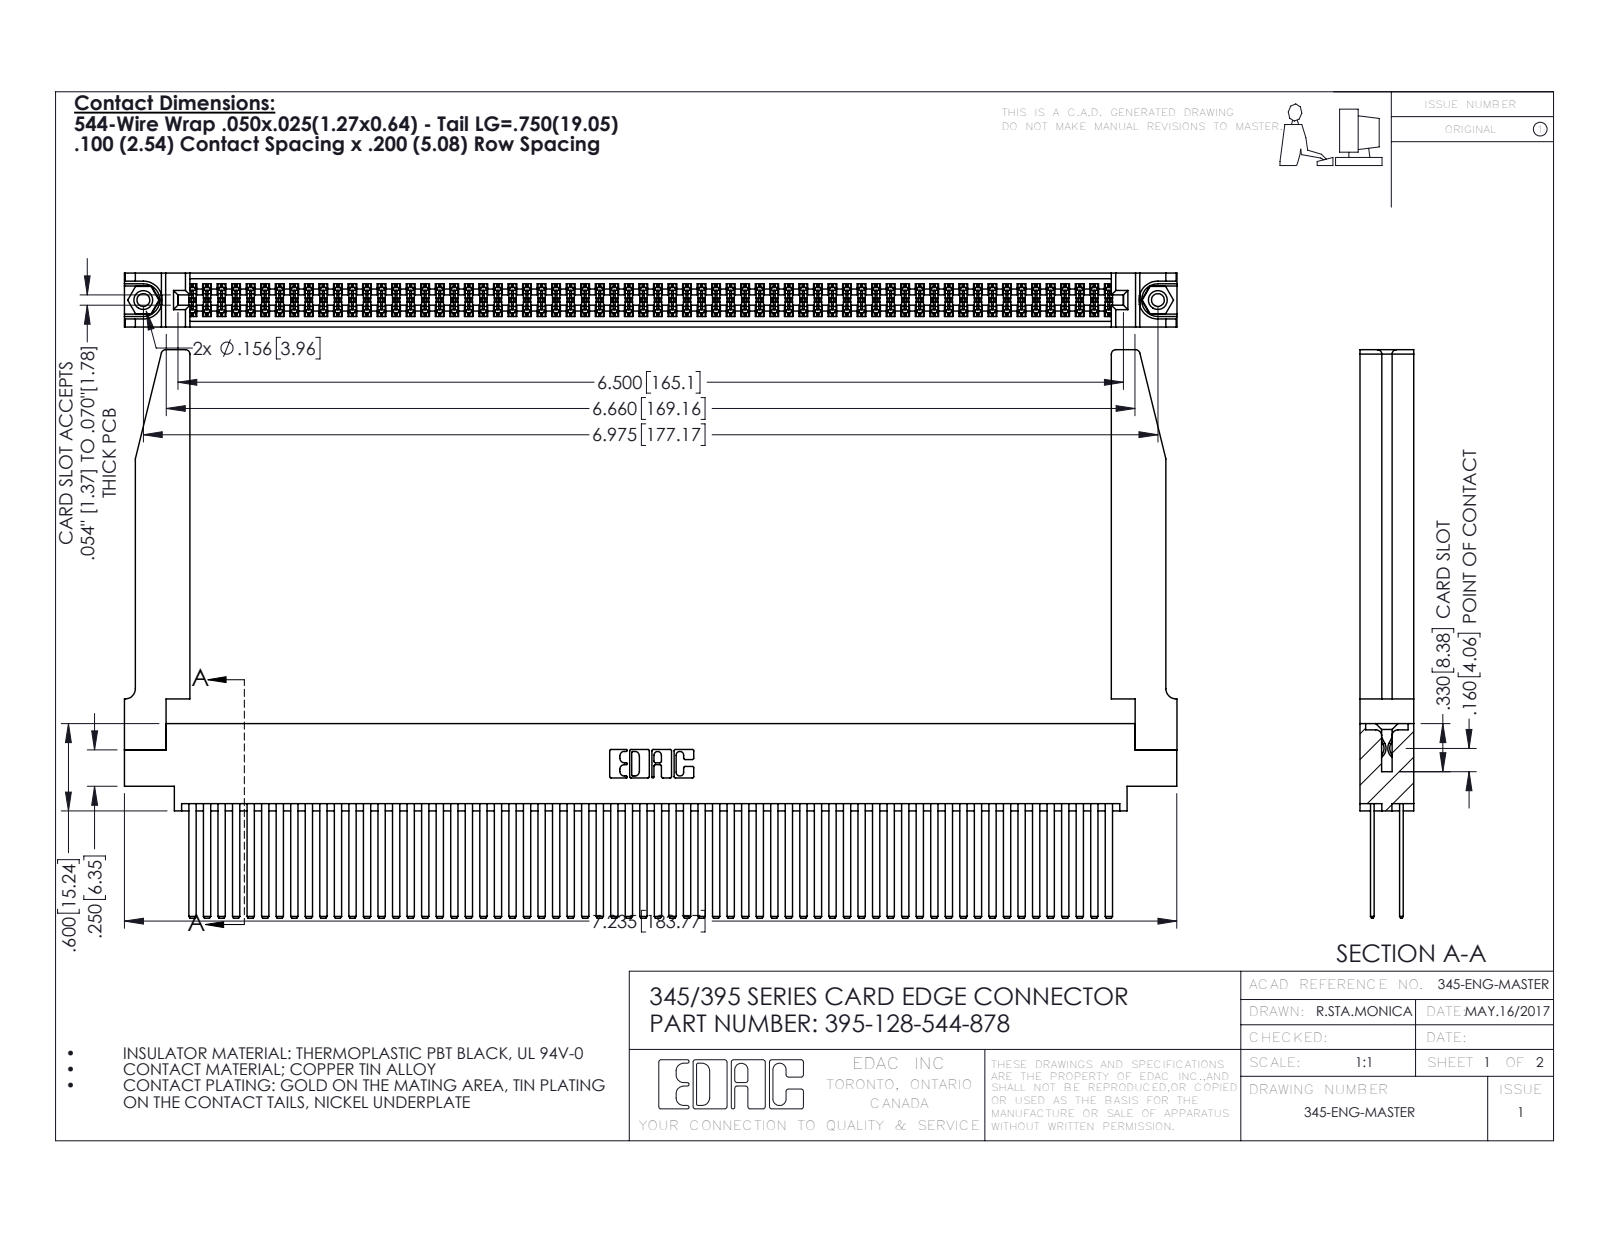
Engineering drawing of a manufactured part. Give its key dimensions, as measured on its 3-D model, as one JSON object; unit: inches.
{"part_name": "345-292-001_345-293-144; 345 Part_0.170 Offset - 0.156 Dia-TH; 345-220-078_345-220-078; 345-250-001_345-250-001-102 (+1 more)", "step_written_by": "SolidWorks 2016 (CONFIG_CONTROL_DESIGN)", "units": "inches", "bodies": {"solids": 133, "faces": 5996, "planar": 3938, "cylindrical": 2006, "other": 52}, "overall_size": [7.236, 3.907, 0.37], "volume_in3": 1.679, "surface_area_in2": 64.86, "round_holes": [[0.089, 2], [0.125, 2], [0.156, 2], [0.064, 1]], "round_bosses_or_shafts": [[0.155, 2]], "partial_cylinders_radius": [[0.006, 192], [0.01, 22], [0.03, 8], [0.007, 6], [0.031, 6], [0.026, 3], [0.014, 2], [0.019, 2]], "face_to_face_distances": [0.072, 0.298, 0.098, 0.272, 0.025, 0.2, 0.37, 0.225, 0.175, 0.148], "hole_center_spacings": [0.27, 6.739, 6.975]}
